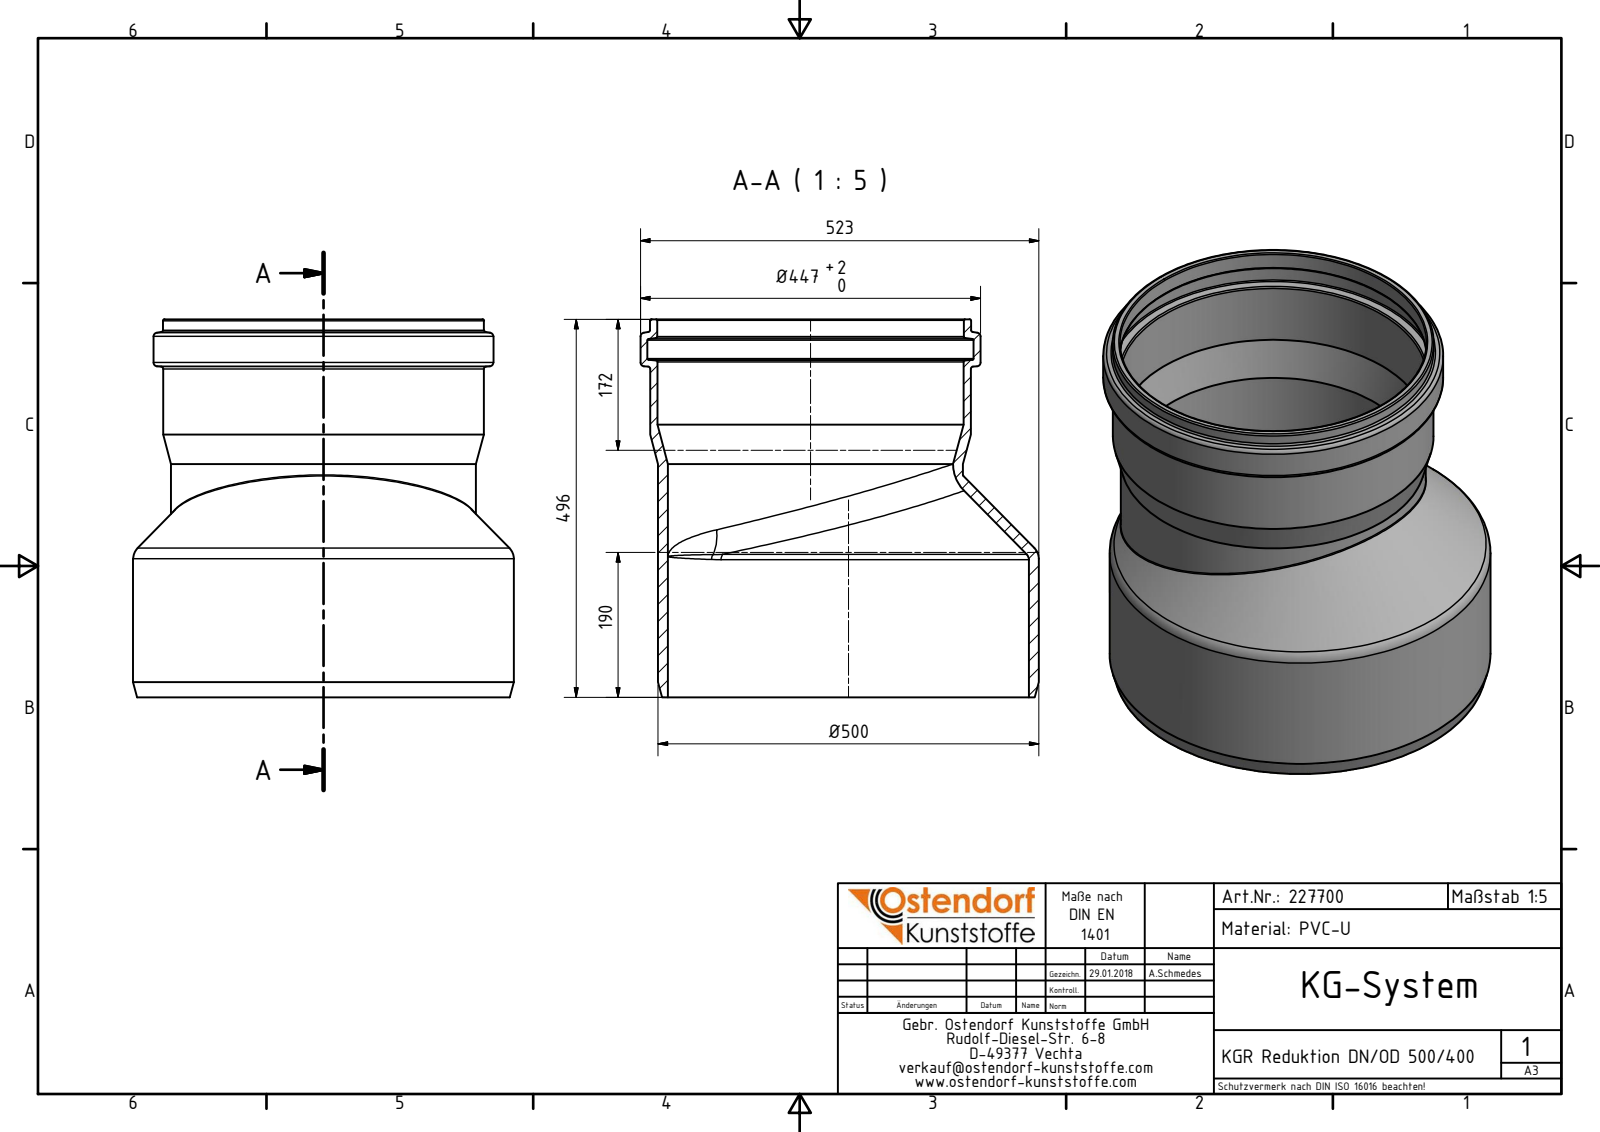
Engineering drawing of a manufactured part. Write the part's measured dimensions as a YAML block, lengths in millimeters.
part_name: "227700 KGR Reduktion DN_OD 500_400"
step_written_by: "Autodesk Inventor 2016 (AUTOMOTIVE_DESIGN)"
units: millimeters
bodies: {solids: 1, faces: 47, planar: 2, cylindrical: 10, other: 35}
overall_size: [523, 500, 496]
volume: 8763000
surface_area: 1510000
round_holes:
  - {diameter: 374.35, count: 1}
  - {diameter: 402, count: 1}
  - {diameter: 402.4, count: 1}
  - {diameter: 428.35, count: 1}
  - {diameter: 474, count: 1}
round_bosses_or_shafts:
  - {diameter: 500, count: 1}
  - {diameter: 446.35, count: 1}
  - {diameter: 421.4, count: 1}
  - {diameter: 421.1, count: 1}
  - {diameter: 400.35, count: 1}
face_to_face_distances: [496]
hole_center_spacings: [49.83]
